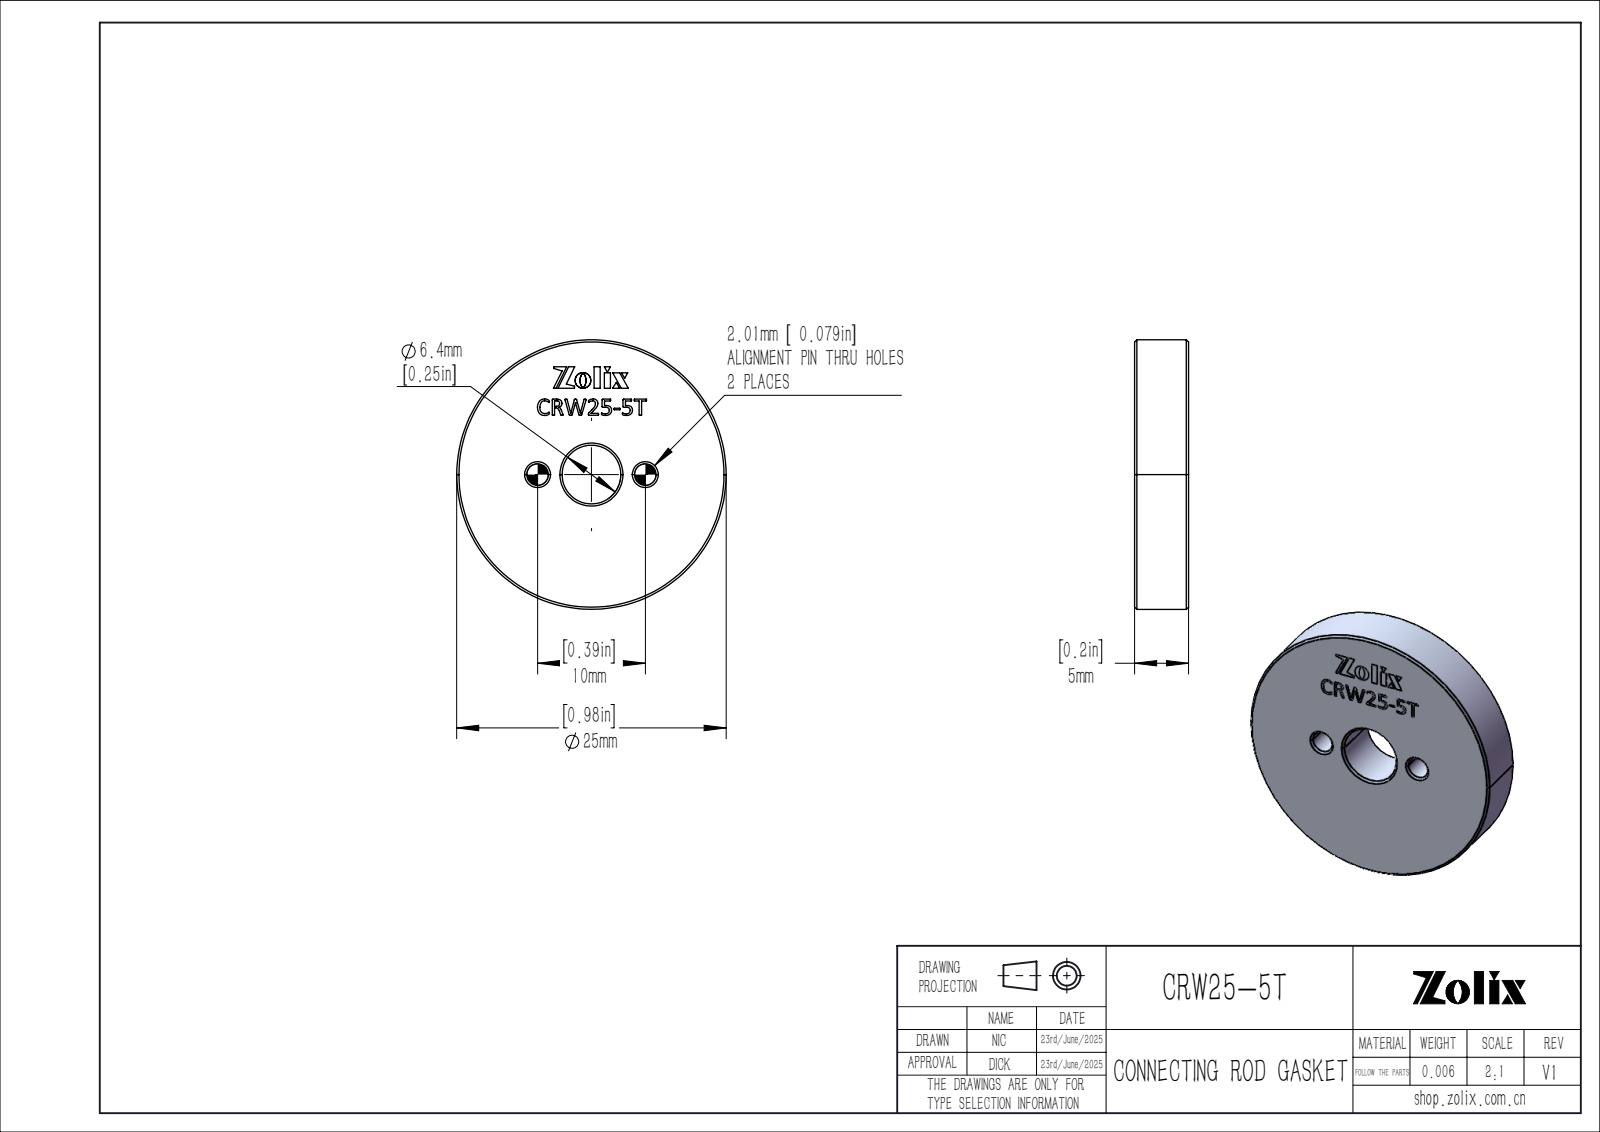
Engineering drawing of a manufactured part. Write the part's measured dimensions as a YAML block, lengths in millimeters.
part_name: "CRW25-5T"
step_written_by: "SolidWorks 2020 (CONFIG_CONTROL_DESIGN)"
units: millimeters
bodies: {solids: 1, faces: 328, planar: 223, cylindrical: 8, other: 97}
overall_size: [25, 25, 5]
volume: 2302
surface_area: 1440
round_holes:
  - {diameter: 2, count: 2}
  - {diameter: 5.45, count: 1}
round_bosses_or_shafts:
  - {diameter: 25, count: 1}
face_to_face_distances: [5, 4.98, 0.56, 2, 1, 3, 8.07, 1.18, 3.18, 1.5]
hole_center_spacings: [5, 10]
